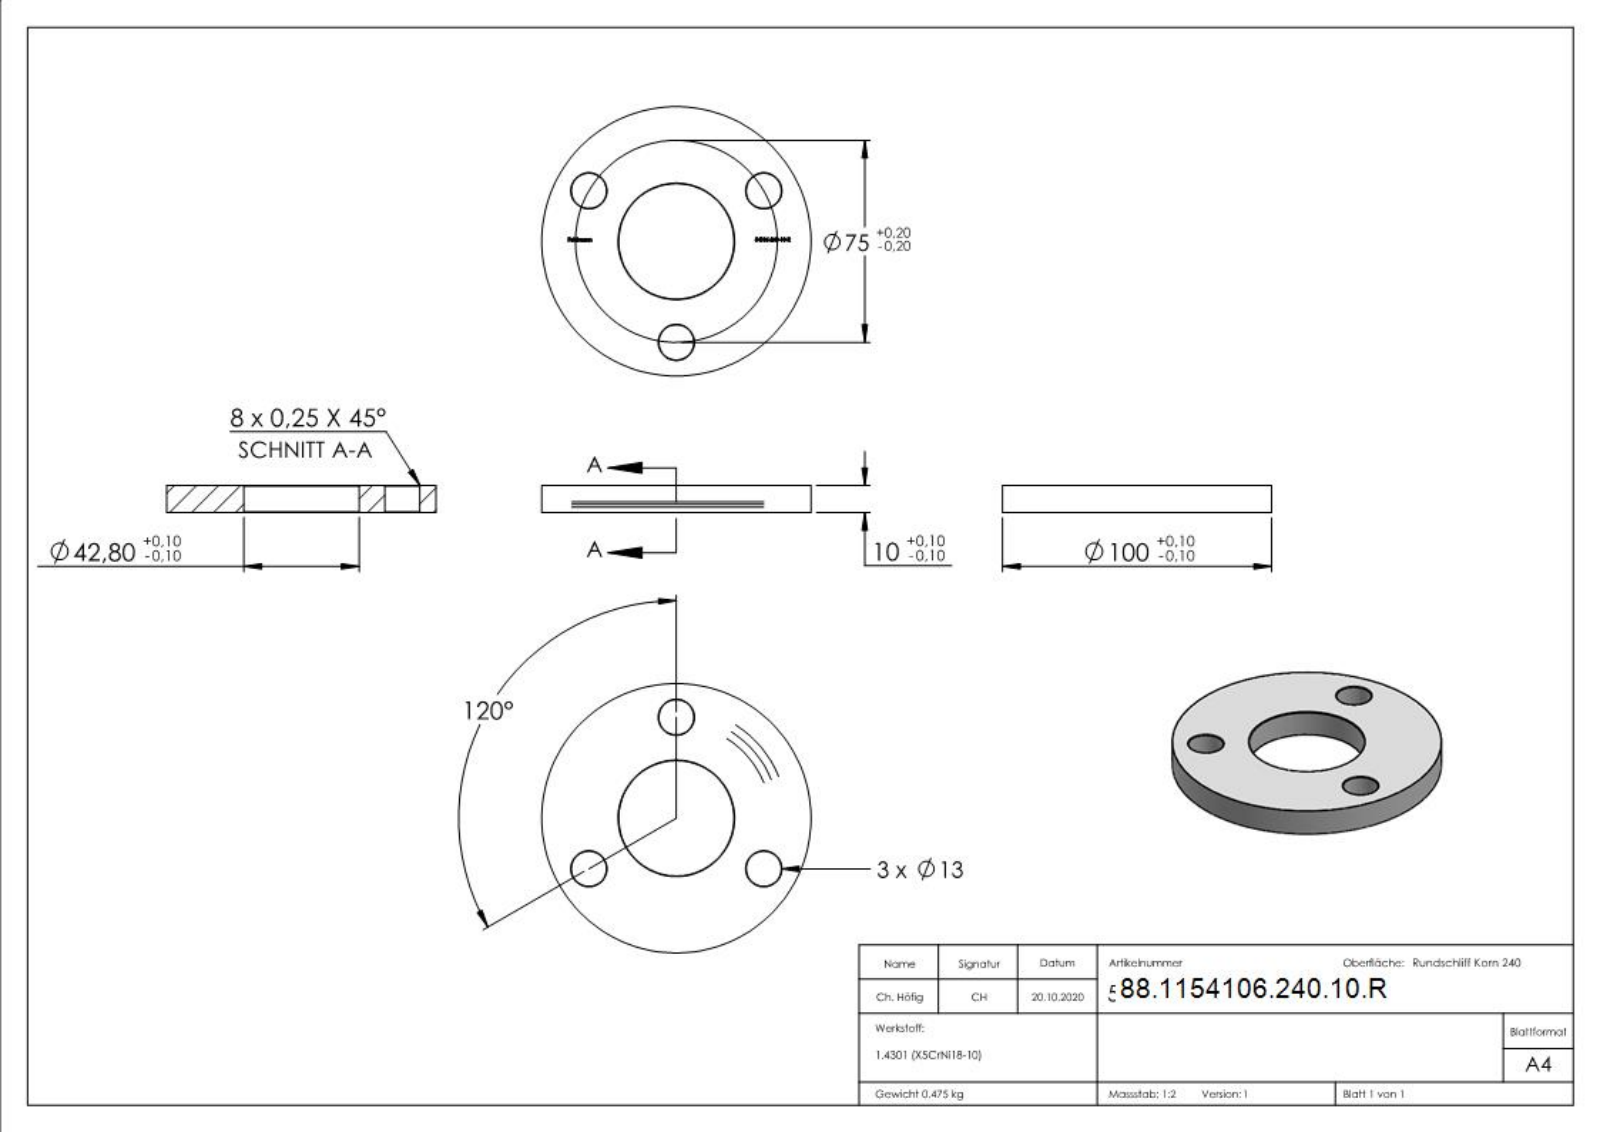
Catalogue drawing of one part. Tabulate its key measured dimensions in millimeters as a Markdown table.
| quantity | value |
| --- | --- |
| part name | 54106-240-10-R |
| STEP written by | SolidWorks 2018 (CONFIG_CONTROL_DESIGN) |
| units | millimeters |
| bodies | 1 solid, 293 faces (164 planar, 10 cylindrical, 119 other) |
| overall size | 100 × 100 × 10 |
| volume | 60 154 mm³ |
| surface area | 17 682 mm² |
| round holes (diameter × count) | 13 × 3, 42.8 × 1 |
| round bosses / shafts (diameter × count) | 100 × 1 |
| main face-to-face distances | 10, 9.9, 0.88, 0.44, 0.58, 69.84, 77.17, 7.33, 2.02, 81.55 |
| hole center spacings | 37.5, 64.95, 64.96 |
